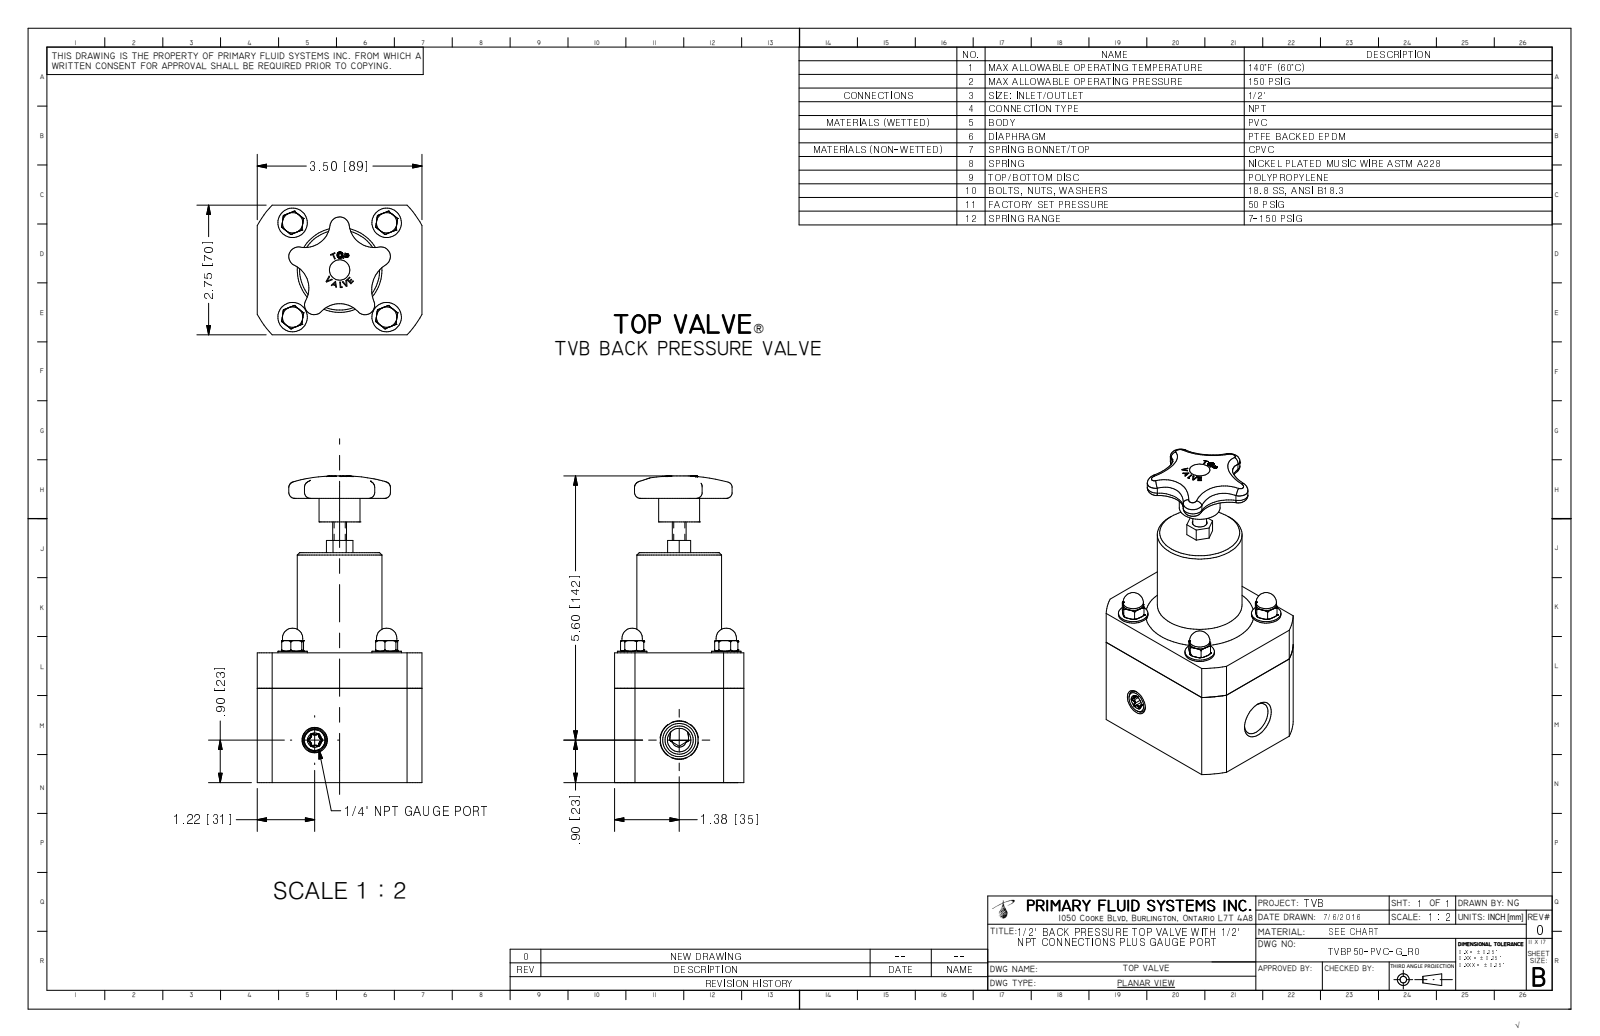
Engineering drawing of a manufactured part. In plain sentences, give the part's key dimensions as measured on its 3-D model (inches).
The part is named "TVBP50-PVC-G_R0". Its 3-D file was written by "Autodesk Inventor 2009 (AUTOMOTIVE_DESIGN)". It is 1 solid with 405 faces: 165 planar, 64 cylindrical and 176 other. Overall it measures 6.502 by 3.5 by 2.75 inches. Its volume is 32.15 cubic inches and its surface area 98.22 square inches. Round holes: 4 of diameter 0.175, 4 of diameter 0.281, 1 of diameter 0.313, 1 of diameter 0.703. Round bosses or shafts: 4 of diameter 0.625, 4 of diameter 0.433, 4 of diameter 0.375, 4 of diameter 0.25, 1 of diameter 1.8, 1 of diameter 0.87, 1 of diameter 0.293. Partial cylindrical surfaces (rounded edges, fillets, slot ends): 6 of radius 0.027, 5 of radius 0.085, 5 of radius 0.205, 4 of radius 0.536, 4 of radius 0.656, 1 of radius 0.625, 1 of radius 0.745, 1 of radius 1.988. The main face-to-face distances are 2.75, 3.5, 2.75, 4.875, 2.125, 0.7, 2.8, 2.786, 0.036, 2.089. The hole center spacings are 1.414, 2, 2.828.
